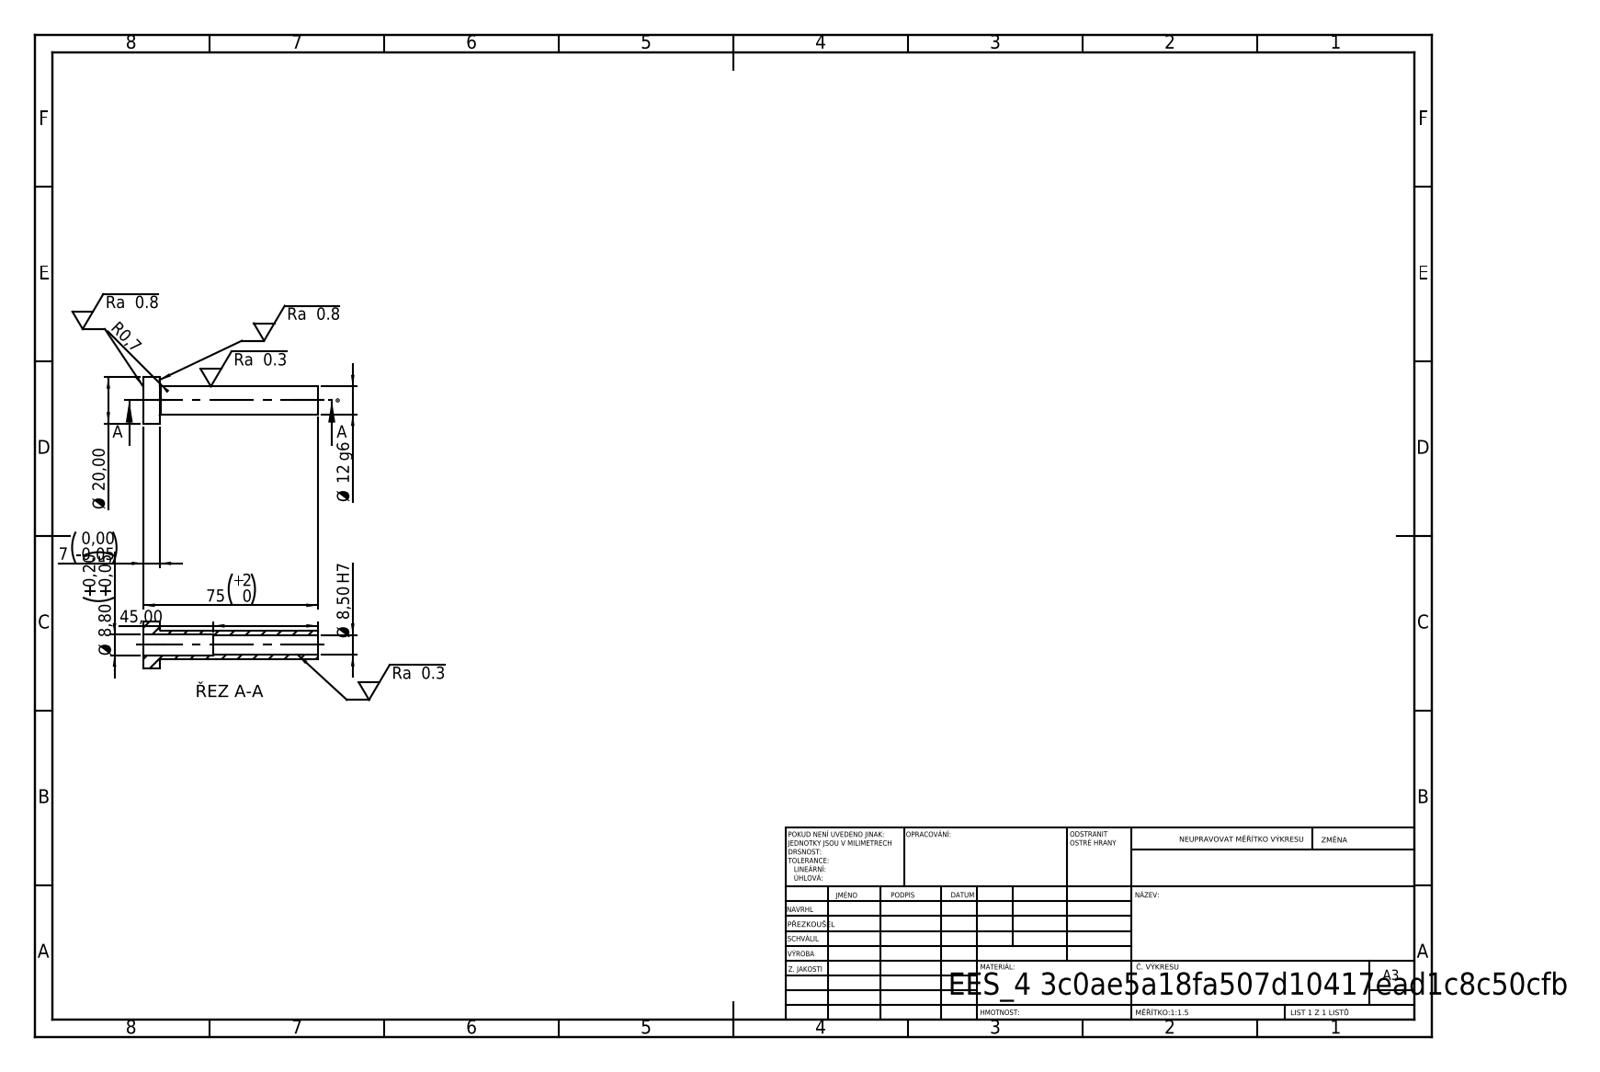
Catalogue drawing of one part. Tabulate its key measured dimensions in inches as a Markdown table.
| quantity | value |
| --- | --- |
| STEP written by | SolidWorks 2019 (CONFIG_CONTROL_DESIGN) |
| units | inches |
| bodies | 1 solid, 14 faces (4 planar, 8 cylindrical, 2 other) |
| overall size | 2.953 × 0.787 × 0.787 |
| volume | 0.337 in³ |
| surface area | 8.584 in² |
| round holes (diameter × count) | 0.335 × 1, 0.346 × 1 |
| round bosses / shafts (diameter × count) | 0.787 × 1, 0.472 × 1 |
| main face-to-face distances | 0.276, 2.953, 2.677, 1.181, 0.906, 1.772 |
